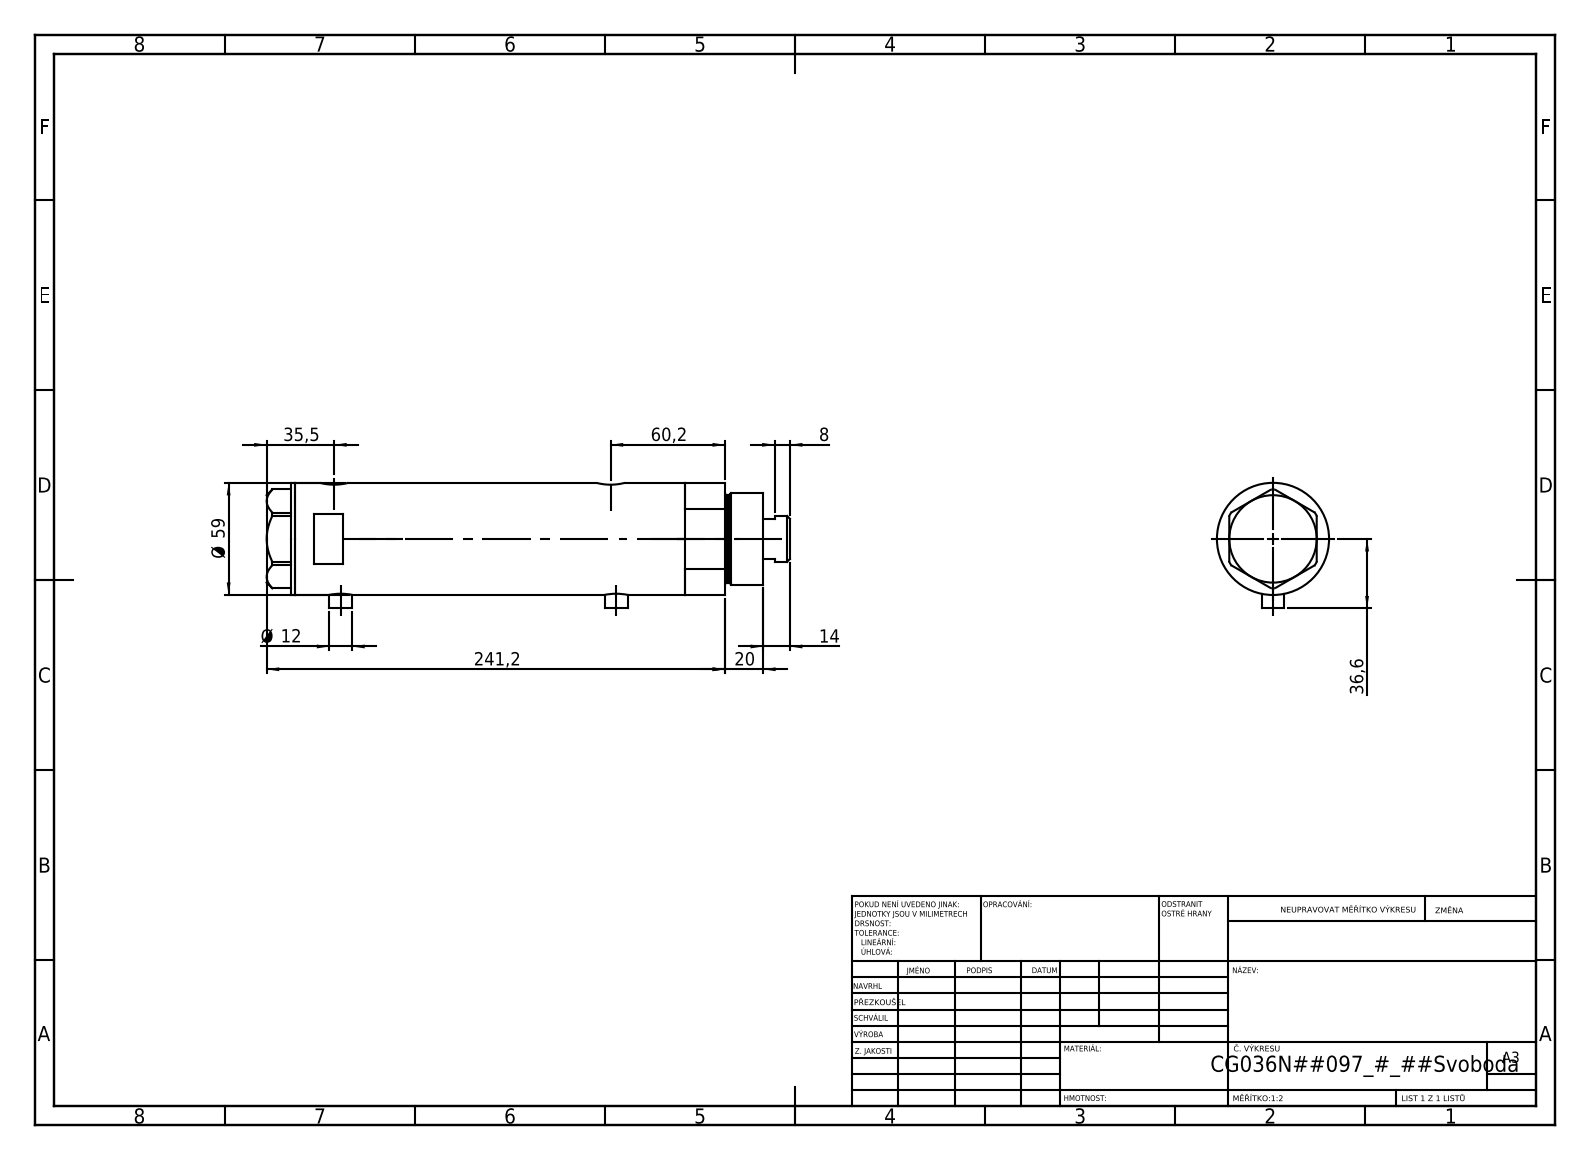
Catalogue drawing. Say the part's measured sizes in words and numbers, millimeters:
The part is named "V270CG_BACK; V270CG_VC; V270CG_FRONT; V270CG_MIDDLE". Its 3-D file was written by "SolidWorks 2019 (CONFIG_CONTROL_DESIGN)". It is 4 solids with 126 faces: 53 planar, 53 cylindrical and 20 other. Overall it measures 275.3 by 66.1 by 59 millimeters. Its volume is 630 417 cubic millimeters and its surface area 125 397 square millimeters. Round holes: 2 of diameter 5, 2 of diameter 9.73, 2 of diameter 12.5, 2 of diameter 15, 1 of diameter 8.5, 1 of diameter 25, 1 of diameter 26.5, 1 of diameter 36, 1 of diameter 40, 1 of diameter 52. Round bosses or shafts: 2 of diameter 12, 1 of diameter 59, 1 of diameter 48, 1 of diameter 46, 1 of diameter 24. The main face-to-face distances are 167.2, 23.5, 143.7, 15, 38.5, 182.2, 2, 246.2, 261.2, 222.7. The hole center spacings are 2.9, 3.5, 142, 144.9, 145.5, 148.4.
